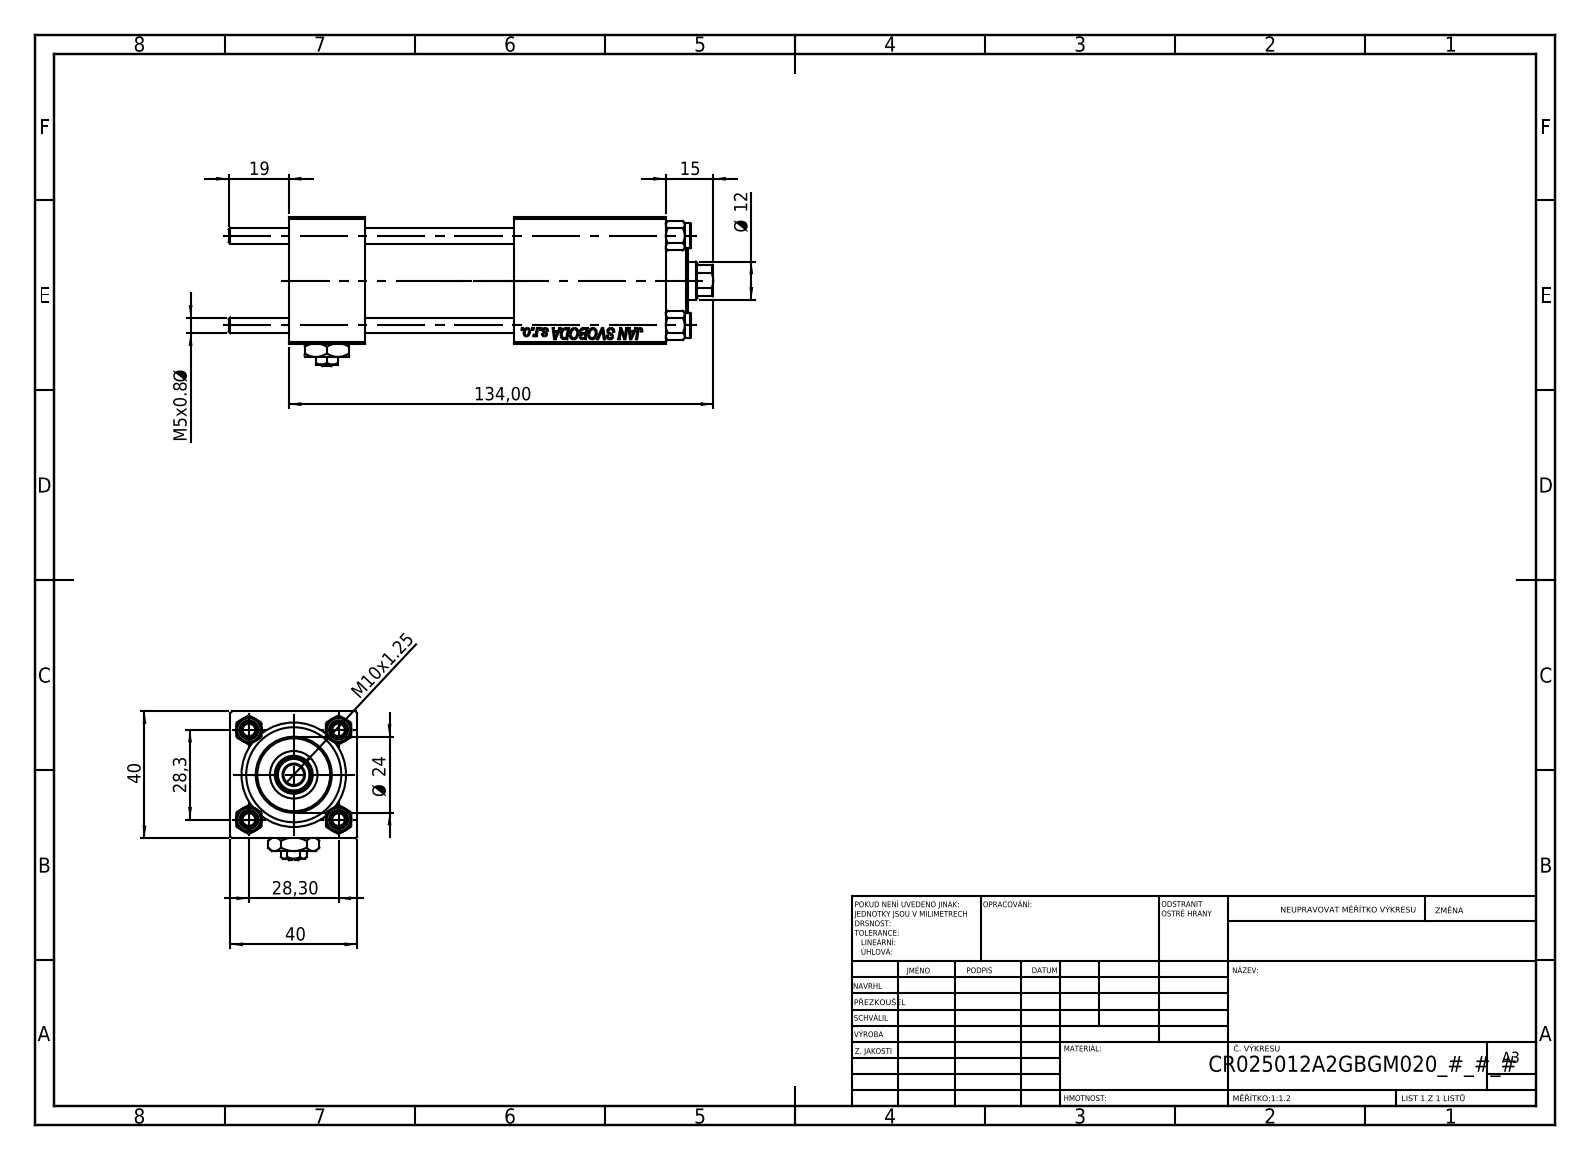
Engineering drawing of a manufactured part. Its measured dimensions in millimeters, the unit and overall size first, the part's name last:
Units: millimetres
Overall size (bounding box): 153 × 47 × 40
Round holes (diameter × count): ⌀5 ×4, ⌀20 ×3, ⌀7 ×2, ⌀13.16 ×2, ⌀6.5 ×1, ⌀12 ×1, ⌀15 ×1, ⌀25 ×1, ⌀30 ×1
Round bosses / shafts (diameter × count): ⌀8 ×4, ⌀31 ×1, ⌀24 ×1
Partial cylindrical surfaces — rounded edges, fillets, slot ends (radius × count): R5.5 ×1
Main face-to-face distances: 40, 24, 119, 95, 90.3, 66.3, 28.7, 47, 71, 19.3
Hole centre spacings: 20.01, 28.3, 40.02, 72
Volume: 144 071 mm³ · Surface area: 59 896 mm²
Bodies: 12 solids, 1184 faces (540 planar, 86 cylindrical, 558 other)
Part name (STEP PRODUCT): Zatka_pro_OIL_PORT; V215_VC_A; CR025_012_A_0_G_A_G_M_020_+#_##_TYCINKA; V215CR_BODY_A (+2 more)
STEP written by: SolidWorks 2019 (CONFIG_CONTROL_DESIGN)
